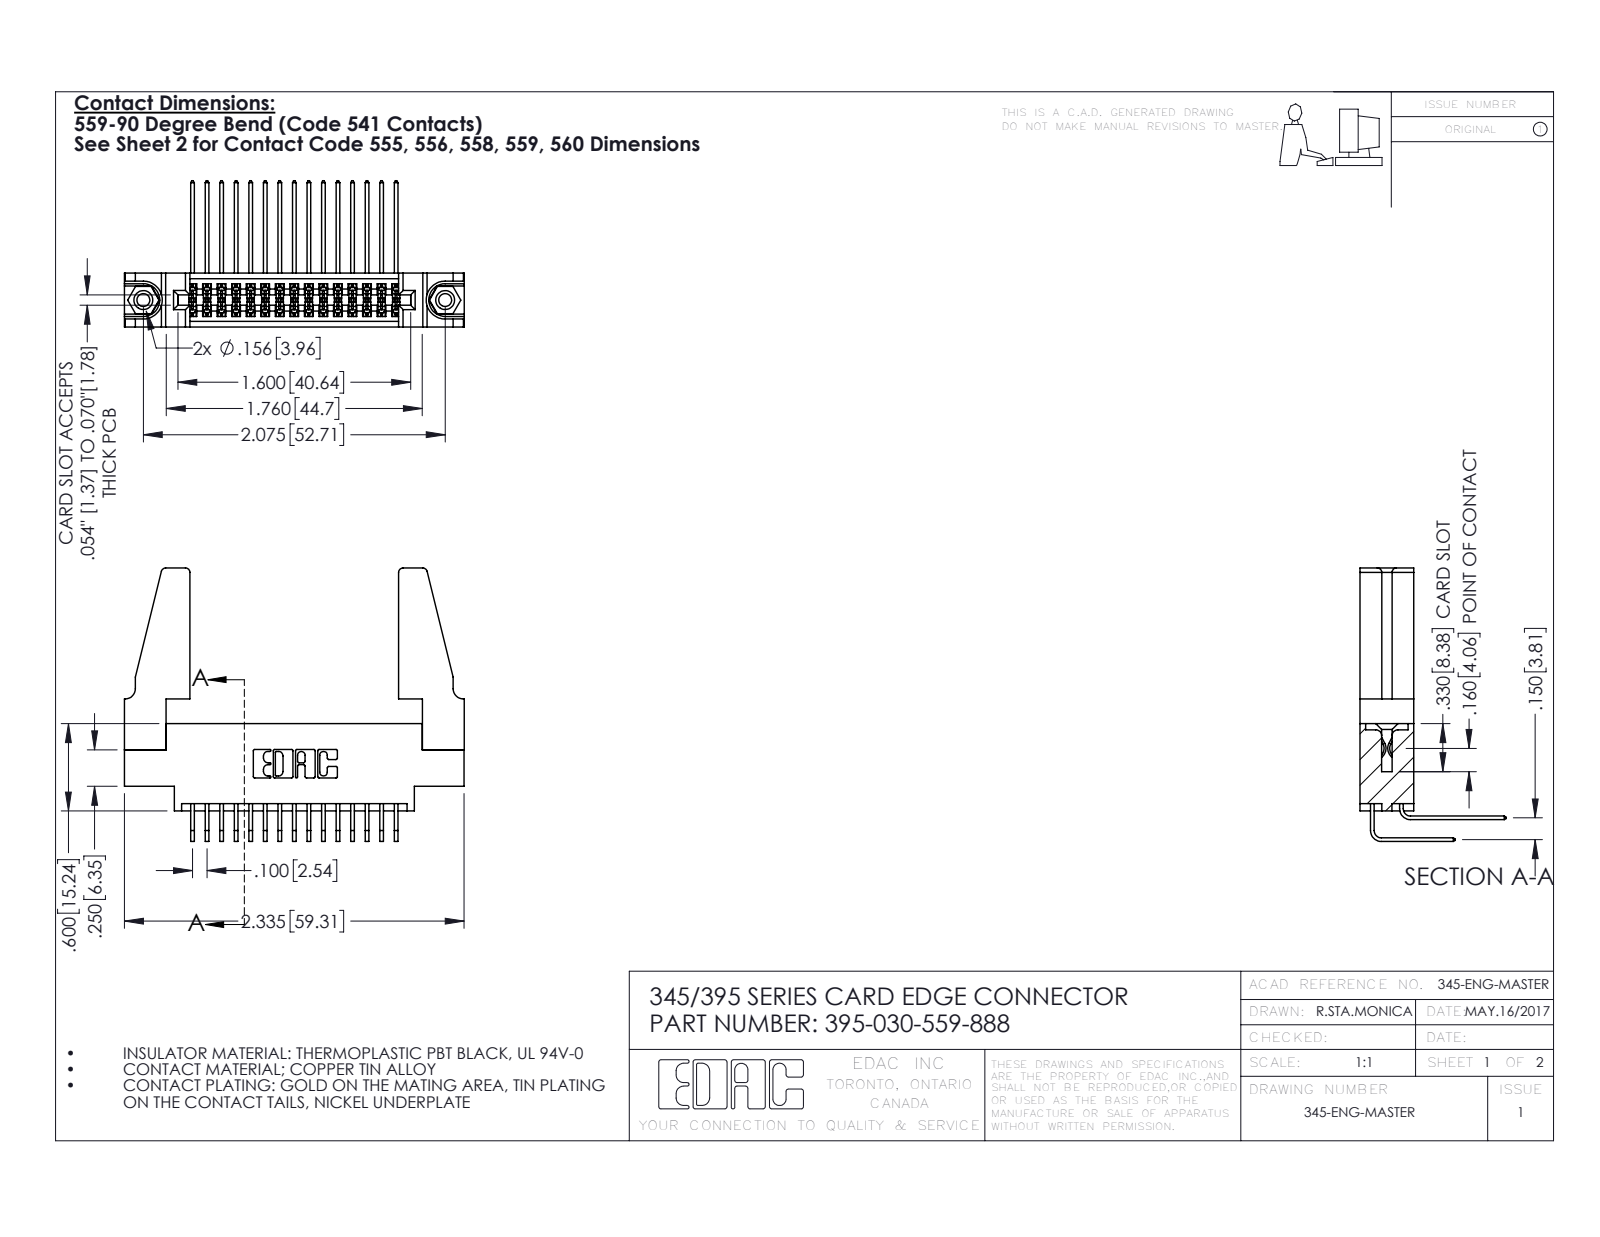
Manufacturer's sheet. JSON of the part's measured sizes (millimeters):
{"part_name": "345-292-001_559 Tail - 2; 395-030-559-888; 345 Part_0.170 Offset - 0.156 Dia-TH; 345-250-001_345-250-001-102 (+2 more)", "step_written_by": "SolidWorks 2016 (CONFIG_CONTROL_DESIGN)", "units": "millimeters", "bodies": {"solids": 35, "faces": 1814, "planar": 1206, "cylindrical": 592, "other": 16}, "overall_size": [59.3, 47.7, 25.5], "volume_mm3": 8830, "surface_area_mm2": 11790, "round_holes": [[2.3, 2], [3.2, 2], [4, 2], [1.6, 1]], "round_bosses_or_shafts": [[3.9, 2]], "partial_cylinders_radius": [[0.2, 45], [0.3, 22], [0.8, 8], [0.2, 6], [0.8, 6], [0.7, 3], [0.4, 2], [0.5, 2]], "face_to_face_distances": [9.4, 1.8, 7.6, 5.1, 2.5, 6.9, 0.6, 3.8, 5.7, 4.4], "hole_center_spacings": [6.9, 46.8, 52.7]}
